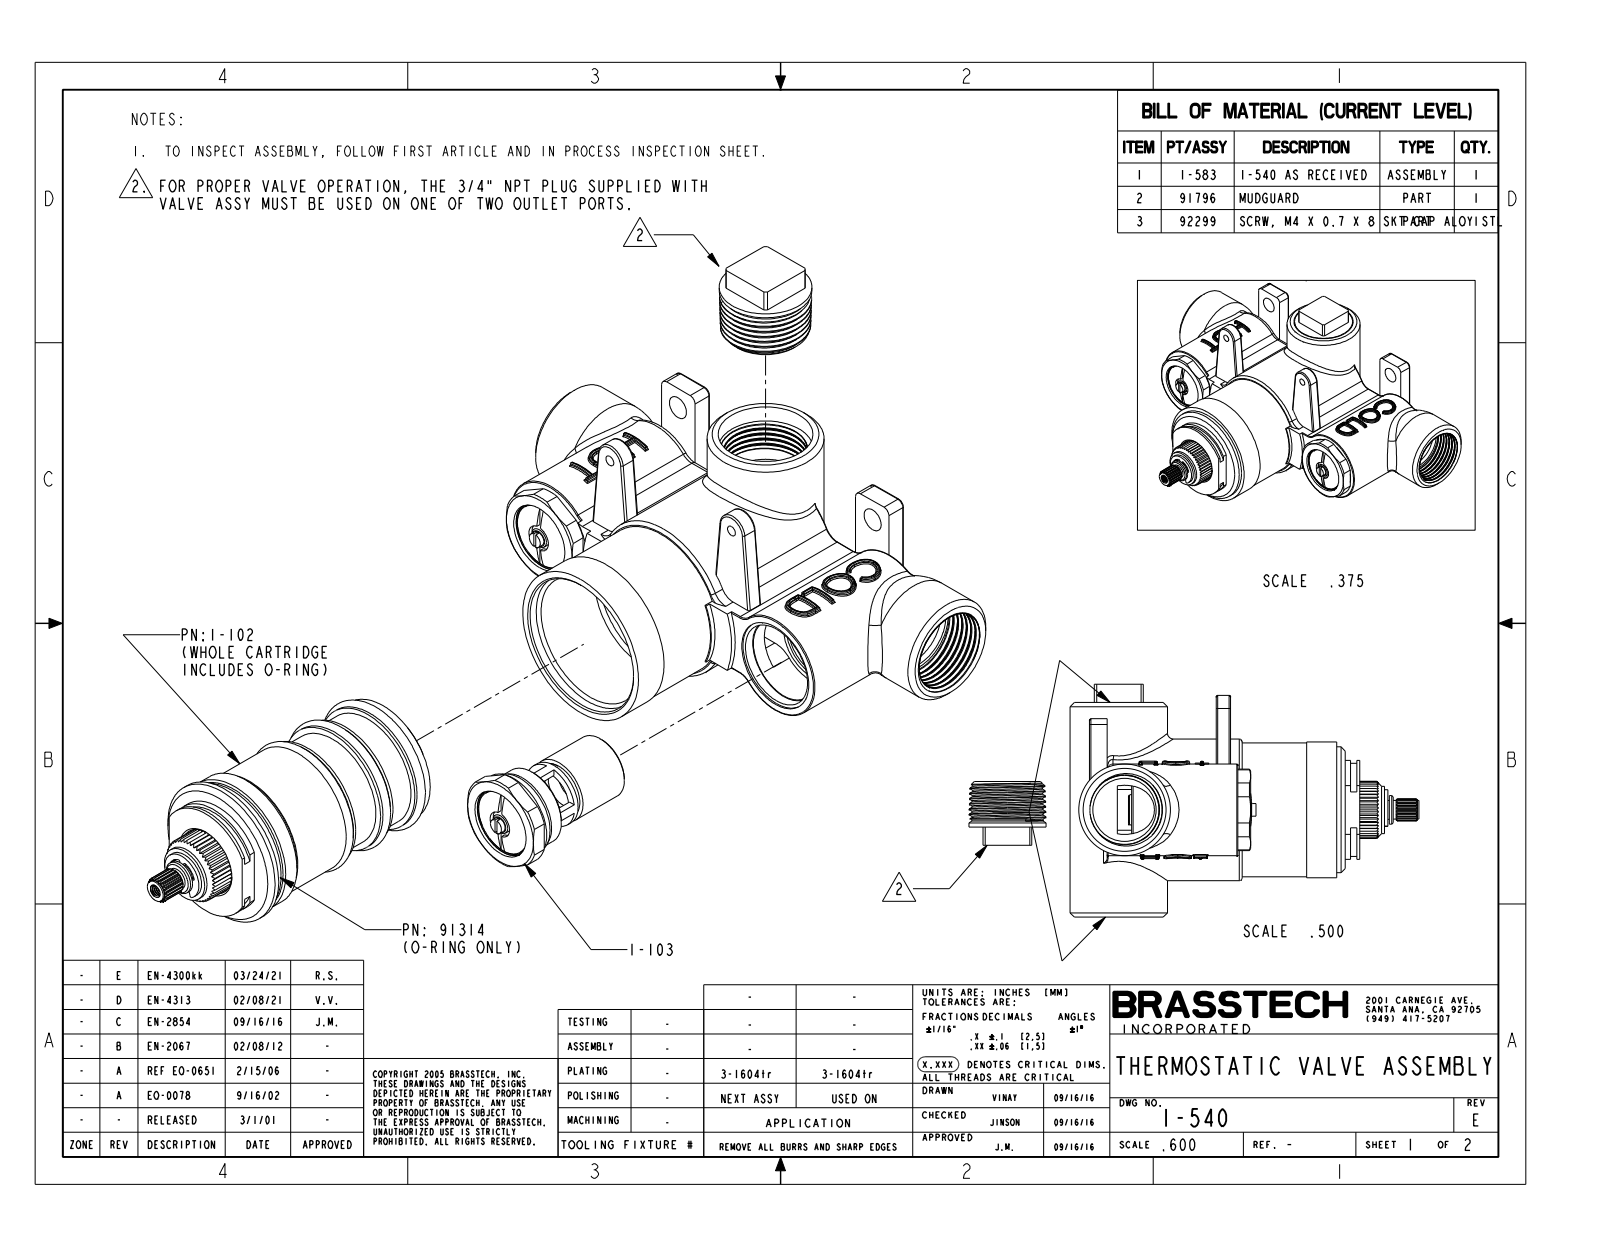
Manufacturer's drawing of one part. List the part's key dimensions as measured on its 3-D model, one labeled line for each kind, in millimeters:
Part name (STEP PRODUCT): VALVE_BODY; 1-103_1; 1-103_6; 1-103_7 (+8 more)
STEP written by: CREO PARAMETRIC BY PTC INC, 2018400 (AUTOMOTIVE_DESIGN)
Units: millimetres
Bodies: 12 solids, 1607 faces (453 planar, 534 cylindrical, 620 other)
Overall size (bounding box): 156 × 121.7 × 81.4
Volume: 316 100 mm³ · Surface area: 81 290 mm²
Round holes (diameter × count): ⌀20.5 ×3, ⌀3.2 ×2, ⌀4.9 ×2, ⌀7 ×2, ⌀8 ×2, ⌀13 ×2, ⌀15.1 ×2, ⌀15.9 ×2, ⌀17.6 ×2, ⌀20 ×2, ⌀21 ×2, ⌀22 ×2
Round bosses / shafts (diameter × count): ⌀27 ×2, ⌀24 ×2, ⌀21.5 ×2, ⌀19.9 ×2, ⌀19.8 ×2, ⌀17.2 ×2, ⌀17 ×2, ⌀15.2 ×2
Partial cylindrical surfaces — rounded edges, fillets, slot ends (radius × count): R0.3 ×77, R0.5 ×30, R1 ×11, R5 ×10, R2 ×8, R8.5 ×4, R2.2 ×2, R14.2 ×2
Main face-to-face distances: 45, 1.5, 80, 34.5, 47.5, 5, 3, 3.5, 40, 42
Hole centre spacings: 18, 26, 41.4, 43, 47, 47.2, 65.8, 80.1
